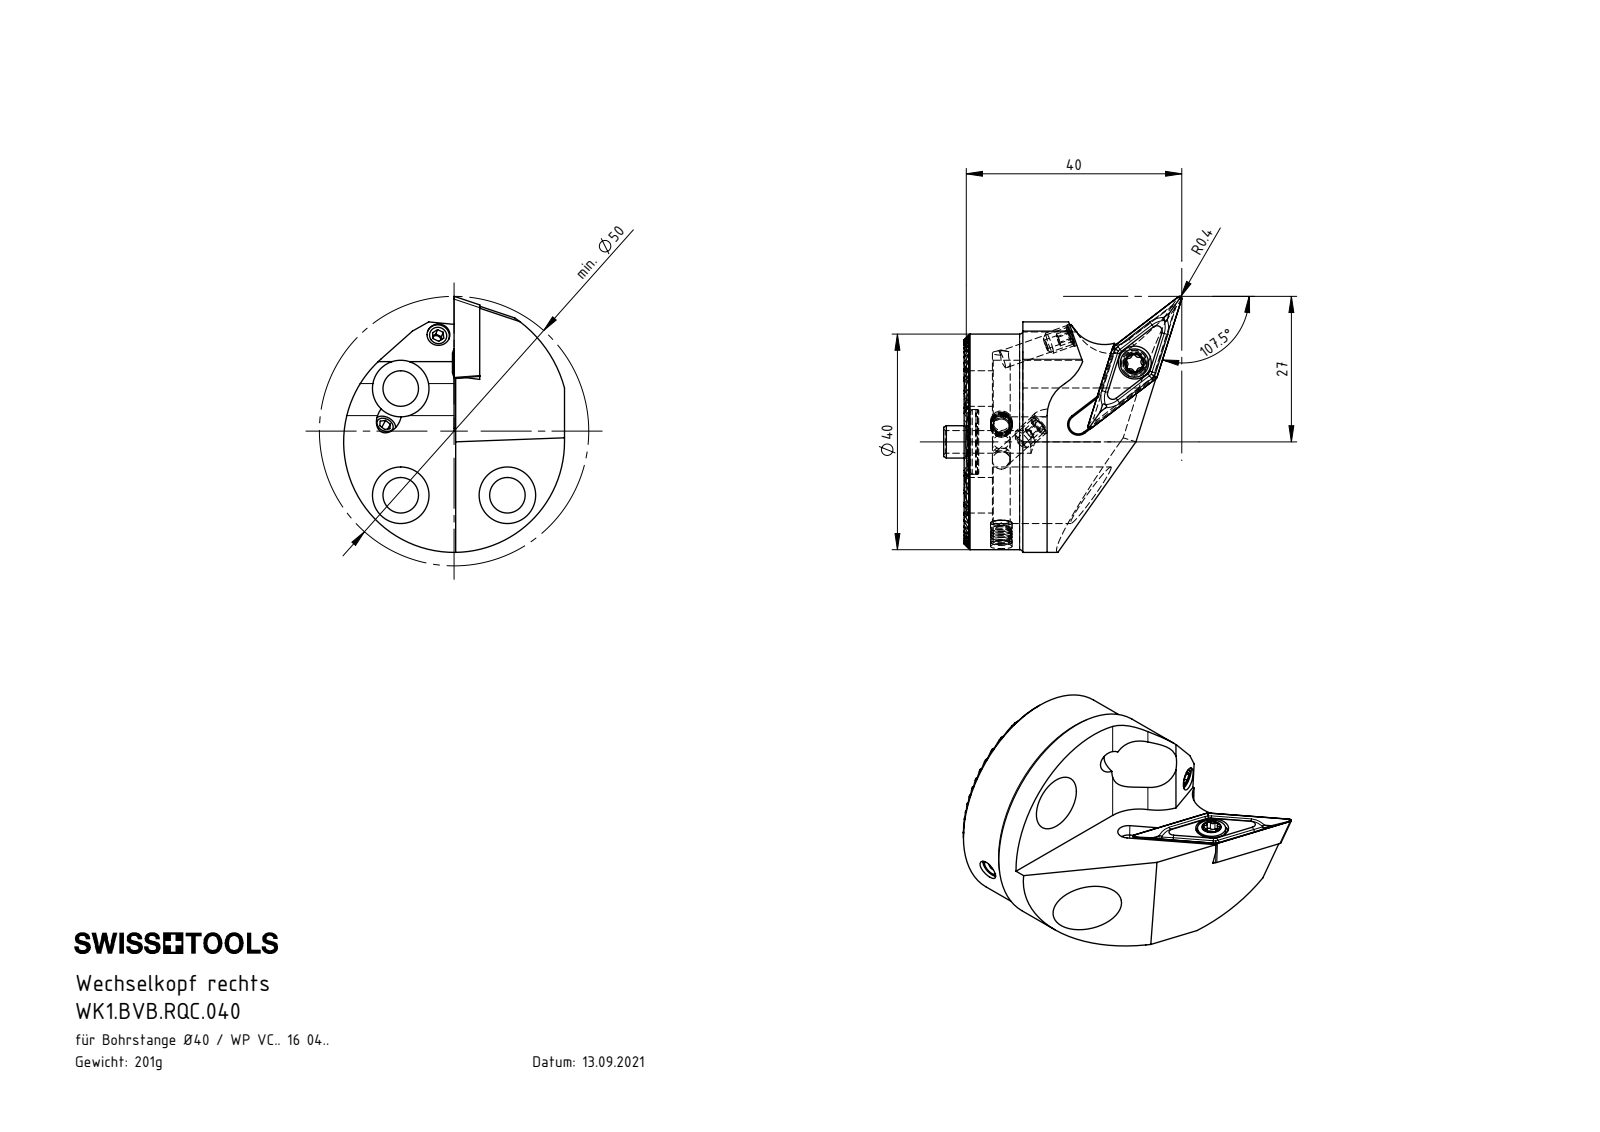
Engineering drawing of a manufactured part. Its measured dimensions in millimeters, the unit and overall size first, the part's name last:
Units: millimetres
Overall size (bounding box): 47.5 × 44.2 × 41
Round holes (diameter × count): ⌀3.3 ×5, ⌀4.2 ×3, ⌀6.6 ×3, ⌀10.5 ×3, ⌀1.7 ×2, ⌀3 ×2, ⌀4 ×1, ⌀4.4 ×1, ⌀6.1 ×1, ⌀12 ×1
Round bosses / shafts (diameter × count): ⌀4 ×5, ⌀40 ×1, ⌀6 ×1, ⌀5.25 ×1
Partial cylindrical surfaces — rounded edges, fillets, slot ends (radius × count): R0.12 ×26, R0.34 ×6, R0.59 ×6, R7 ×2, R1.75 ×1, R8 ×1, R20.5 ×1, R23 ×1
Main face-to-face distances: 1.3, 2.6, 3.9, 12.99, 5.2, 11.69, 9.09, 10.39, 7.79, 6.5
Hole centre spacings: 14, 19.8, 28
Volume: 25 212 mm³ · Surface area: 11 311 mm²
Bodies: 10 solids, 416 faces (218 planar, 107 cylindrical, 91 other)
Part name (STEP PRODUCT): WK1.BVB.RQC.040; KVT_MB_600_040; WK2-ER1.001.012_A_Fertigbearbeitung; WCB-ER2.001.009_A (+3 more)
STEP written by: SolidWorks 2017 (AUTOMOTIVE_DESIGN)
